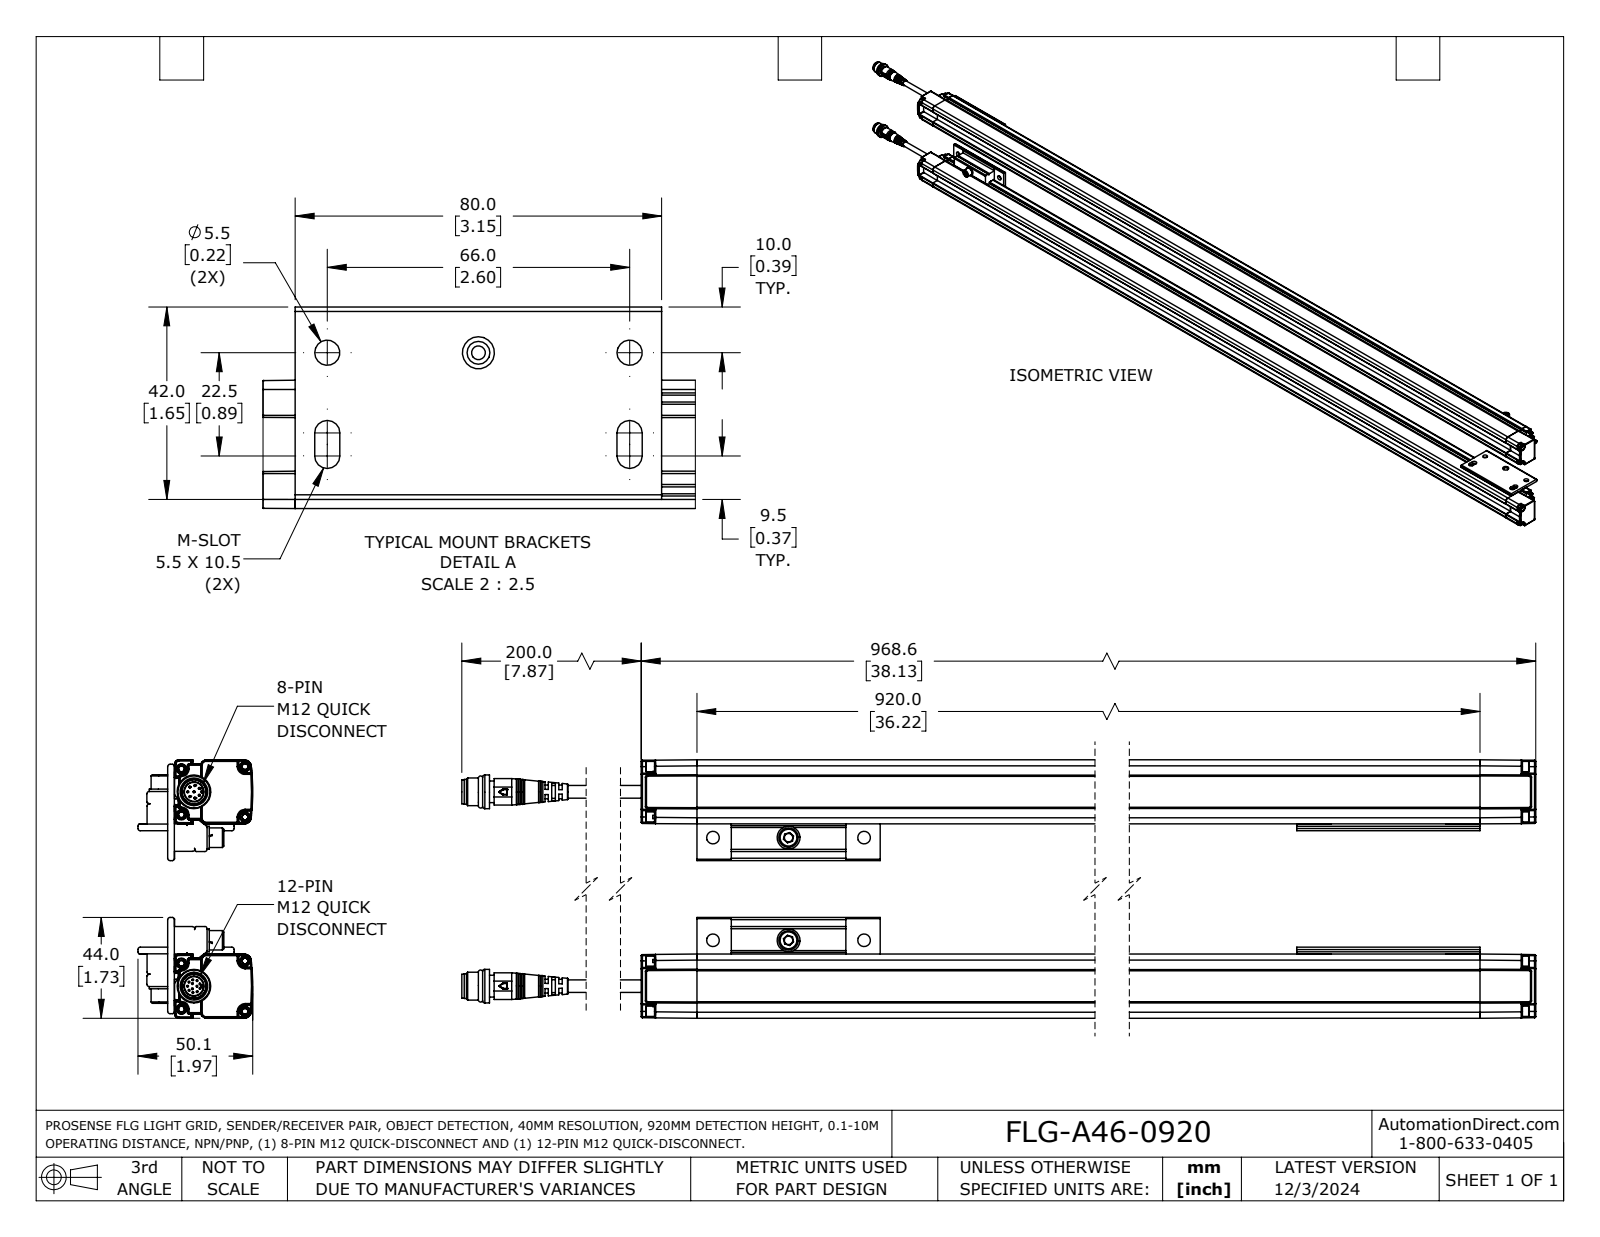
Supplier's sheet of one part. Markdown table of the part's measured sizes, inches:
| quantity | value |
| --- | --- |
| part name | FLG-A46-0920 |
| STEP written by | SolidWorks 2023 (AUTOMOTIVE_DESIGN) |
| units | inches |
| bodies | 5 solids, 869 faces (435 planar, 238 cylindrical, 196 other) |
| overall size | 41.754 × 1.972 × 1.732 |
| volume | 48.05 in³ |
| surface area | 307.6 in² |
| round holes (diameter × count) | 0.016 × 16, 0.217 × 4, 0.098 × 2, 0.197 × 2, 0.327 × 1 |
| round bosses / shafts (diameter × count) | 0.031 × 8, 0.177 × 4, 0.118 × 4, 0.394 × 2, 0.335 × 2, 0.217 × 2, 0.146 × 2, 0.059 × 2 |
| partial cylindrical surfaces (radius × count) | 0.02 × 76, 0.039 × 20, 0.01 × 10, 0.108 × 8, 0.008 × 6, 0.012 × 6, 0.1 × 4, 0.049 × 2 |
| main face-to-face distances | 1.102, 0.071, 0.817, 0.285, 0.97, 1.041, 0.215, 1.031, 0.746, 0.531 |
| hole center spacings | 0.108, 0.163, 1.299, 0.215, 0.089, 0.09, 0.09, 0.118 |
